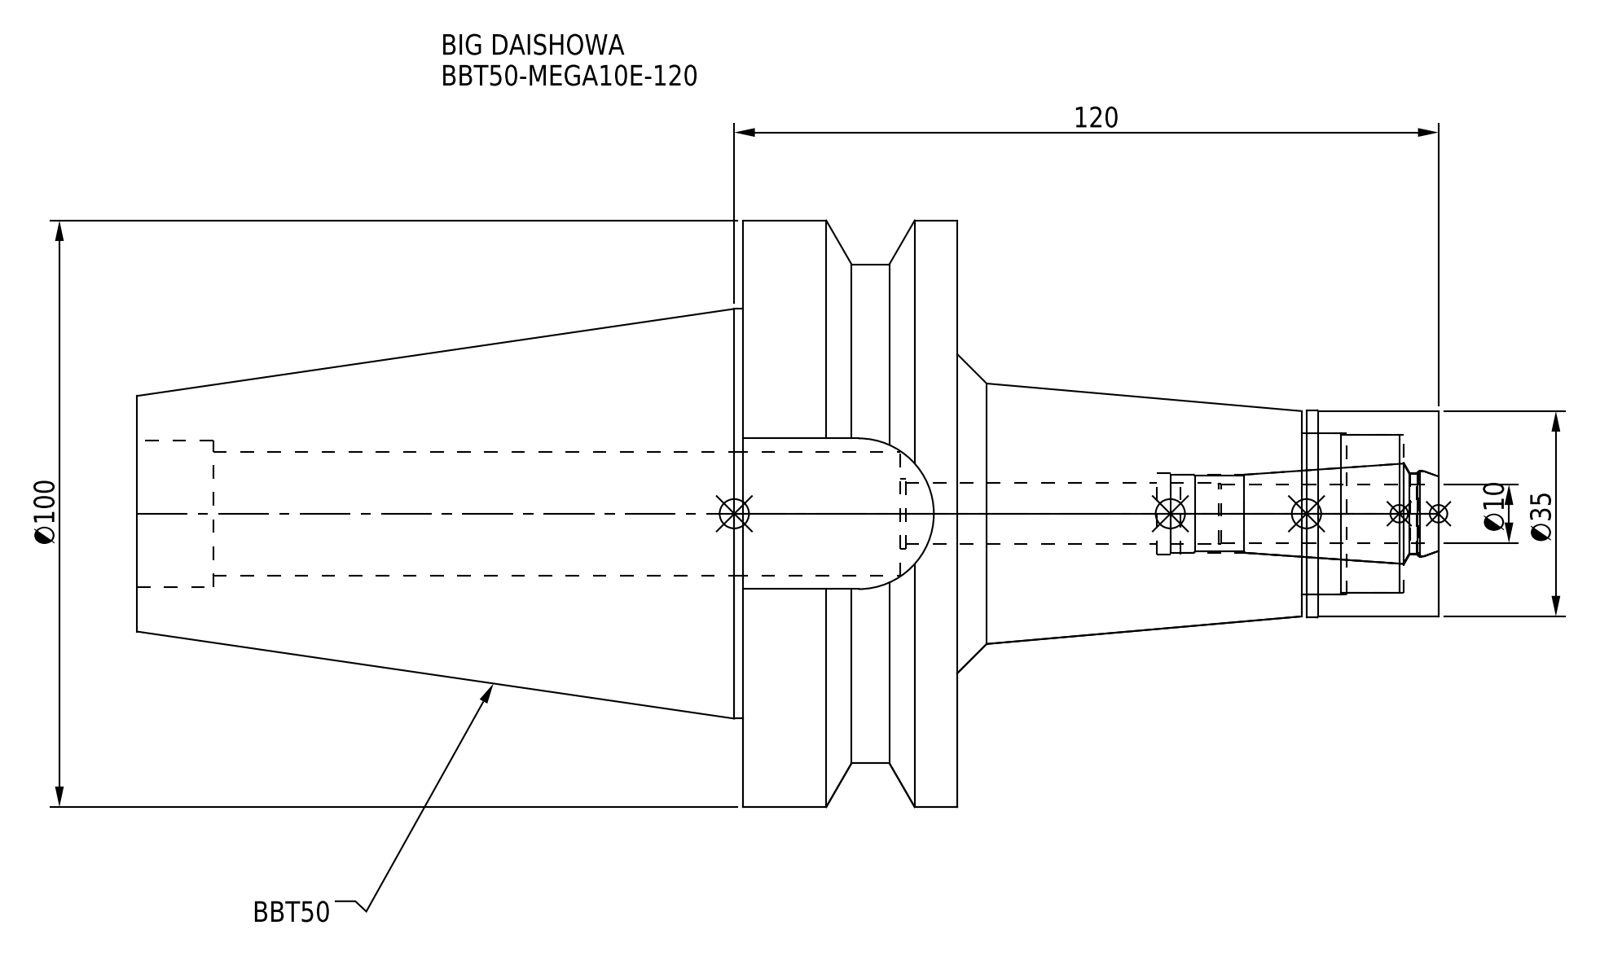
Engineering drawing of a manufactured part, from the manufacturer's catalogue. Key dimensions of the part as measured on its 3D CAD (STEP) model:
Part name (STEP PRODUCT): BBT50-MEGA10E-120_1.stp; MEN10_1.stp; BBT50ME10120-100_ASM.stp; BBT50-MEGA10E-120 (+3 more)
STEP written by: SolidWorks 2019 (CONFIG_CONTROL_DESIGN)
Units: millimetres
Bodies: 2 solids, 81 faces (21 planar, 40 cylindrical, 20 other)
Overall size (bounding box): 221.8 × 100 × 100
Volume: 537 812 mm³ · Surface area: 70 940 mm²
Round holes (diameter × count): ⌀10.4 ×1, ⌀12 ×1, ⌀13.3 ×1, ⌀13.8 ×1, ⌀13.9 ×1, ⌀14.7 ×1, ⌀21.2 ×1, ⌀25 ×1, ⌀27 ×1, ⌀27.5 ×1
Round bosses / shafts (diameter × count): ⌀100 ×1, ⌀85 ×1, ⌀69.85 ×1, ⌀35.3 ×1, ⌀35 ×1
Partial cylindrical surfaces — rounded edges, fillets, slot ends (radius × count): R12.85 ×1
Main face-to-face distances: 36.5, 82, 118.5, 221.8, 139.8, 103.3, 70.8, 25.7, 22.5, 59.5
